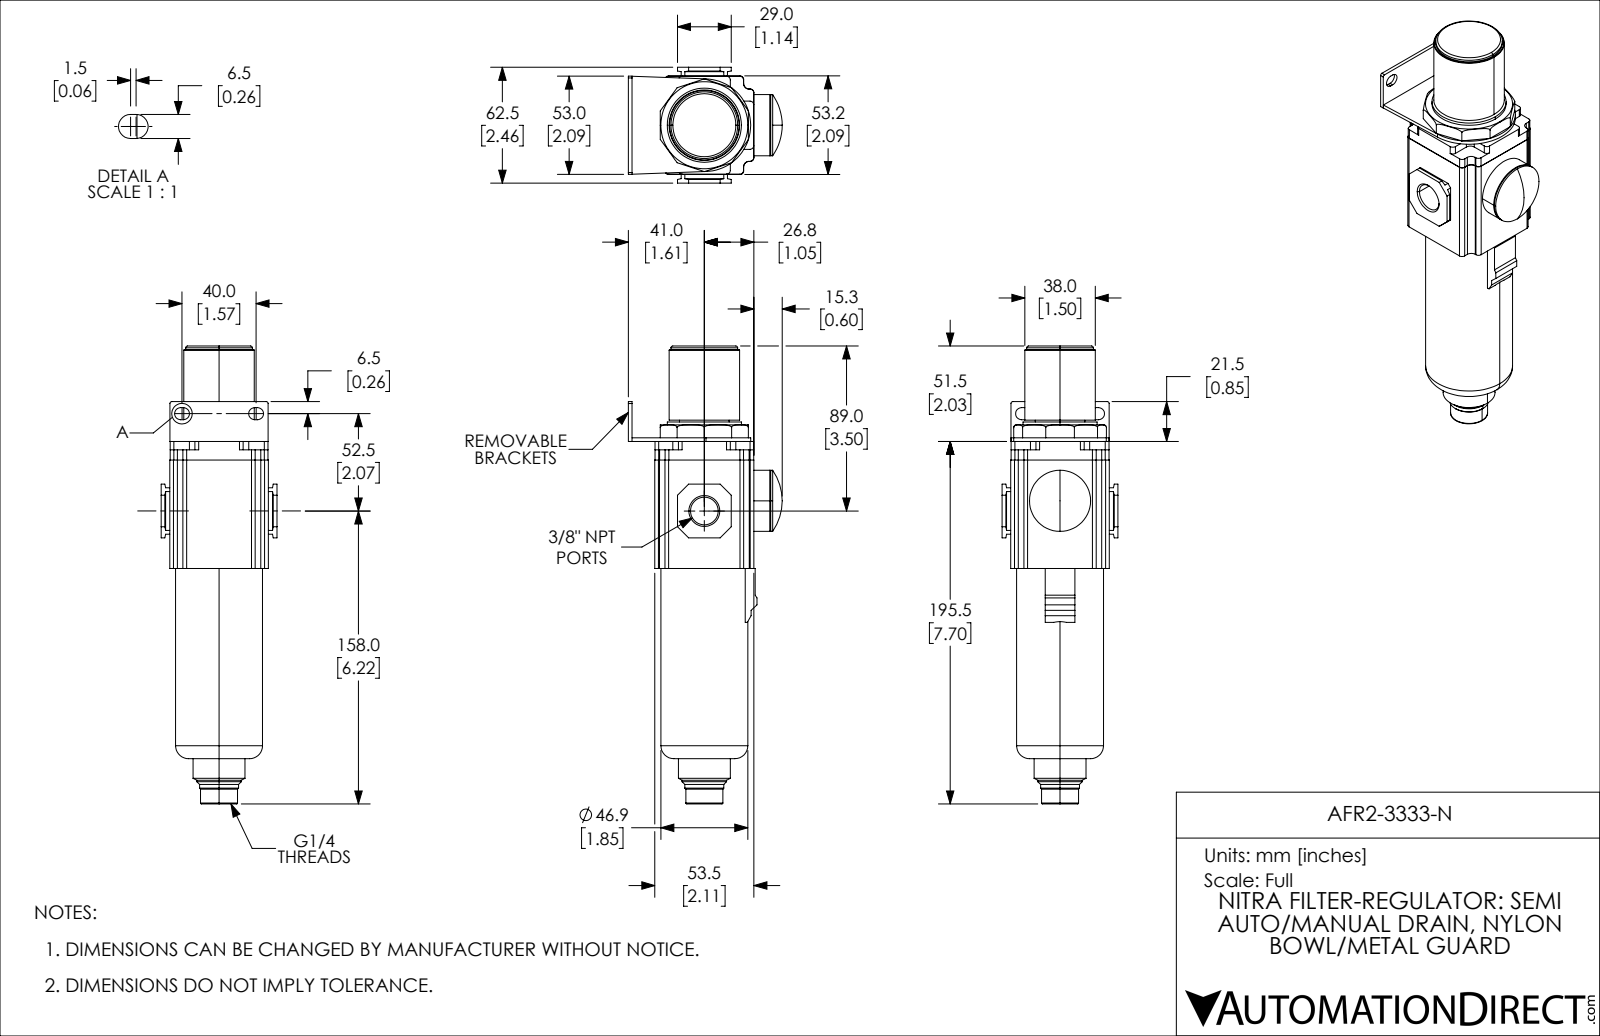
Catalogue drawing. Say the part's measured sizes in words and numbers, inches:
The part is named "AFR2-3333-N". Its 3-D file was written by "SolidWorks 2019 (CONFIG_CONTROL_DESIGN)". It is 1 solid with 221 faces: 124 planar, 71 cylindrical and 26 other. Overall it measures 9.724 by 3.269 by 2.461 inches. Its volume is 27.43 cubic inches and its surface area 80.97 square inches. Round holes: 1 of diameter 0.451, 1 of diameter 0.589. Round bosses or shafts: 1 of diameter 1.846, 1 of diameter 1.575, 1 of diameter 1.496, 1 of diameter 1.417, 1 of diameter 1.299, 1 of diameter 1.102, 1 of diameter 1.054, 1 of diameter 0.945. Partial cylindrical surfaces (rounded edges, fillets, slot ends): 24 of radius 0.079, 12 of radius 0.118, 4 of radius 0.128, 2 of radius 0.039, 1 of radius 0.984. The main face-to-face distances are 0.079, 2.094, 2.106, 0.561, 0.183, 2.278, 0.482, 2.667, 2.028, 1.949.
